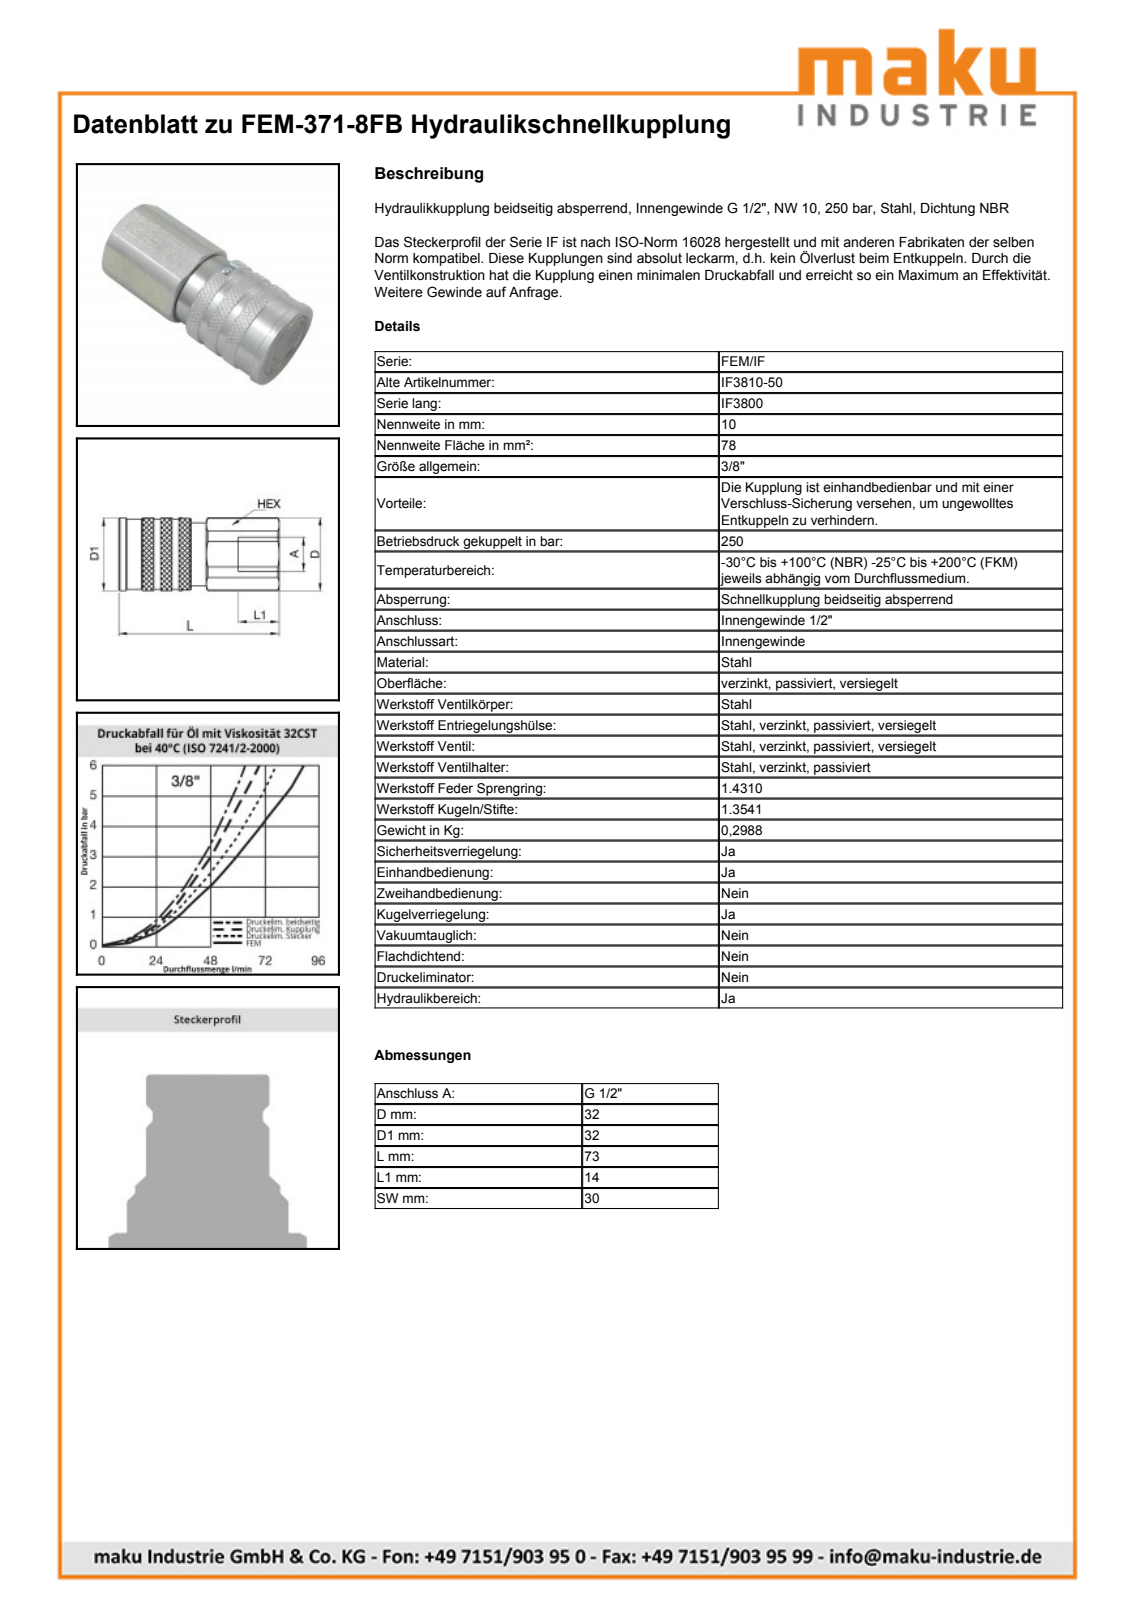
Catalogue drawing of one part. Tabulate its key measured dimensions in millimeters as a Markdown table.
| quantity | value |
| --- | --- |
| part name | FEM-371-8FB |
| STEP written by | SolidWorks 2009 (AUTOMOTIVE_DESIGN) |
| units | millimeters |
| bodies | 1 solid, 110 faces (29 planar, 47 cylindrical, 34 other) |
| overall size | 72.5 × 32 × 32 |
| volume | 49 550 mm³ |
| surface area | 11 277 mm² |
| round holes (diameter × count) | 2 × 1, 12.65 × 1, 18.63 × 1, 19.85 × 1, 24.5 × 1, 28.2 × 1 |
| round bosses / shafts (diameter × count) | 32 × 1, 30.8 × 1, 27.7 × 1, 27.14 × 1, 24.3 × 1, 19.75 × 1, 12.5 × 1 |
| partial cylindrical surfaces (radius × count) | 0.5 × 2, 12.74 × 1 |
| main face-to-face distances | 30, 72.5, 72, 0.5, 16.93, 55.07, 55.57, 34, 17.07, 38 |
